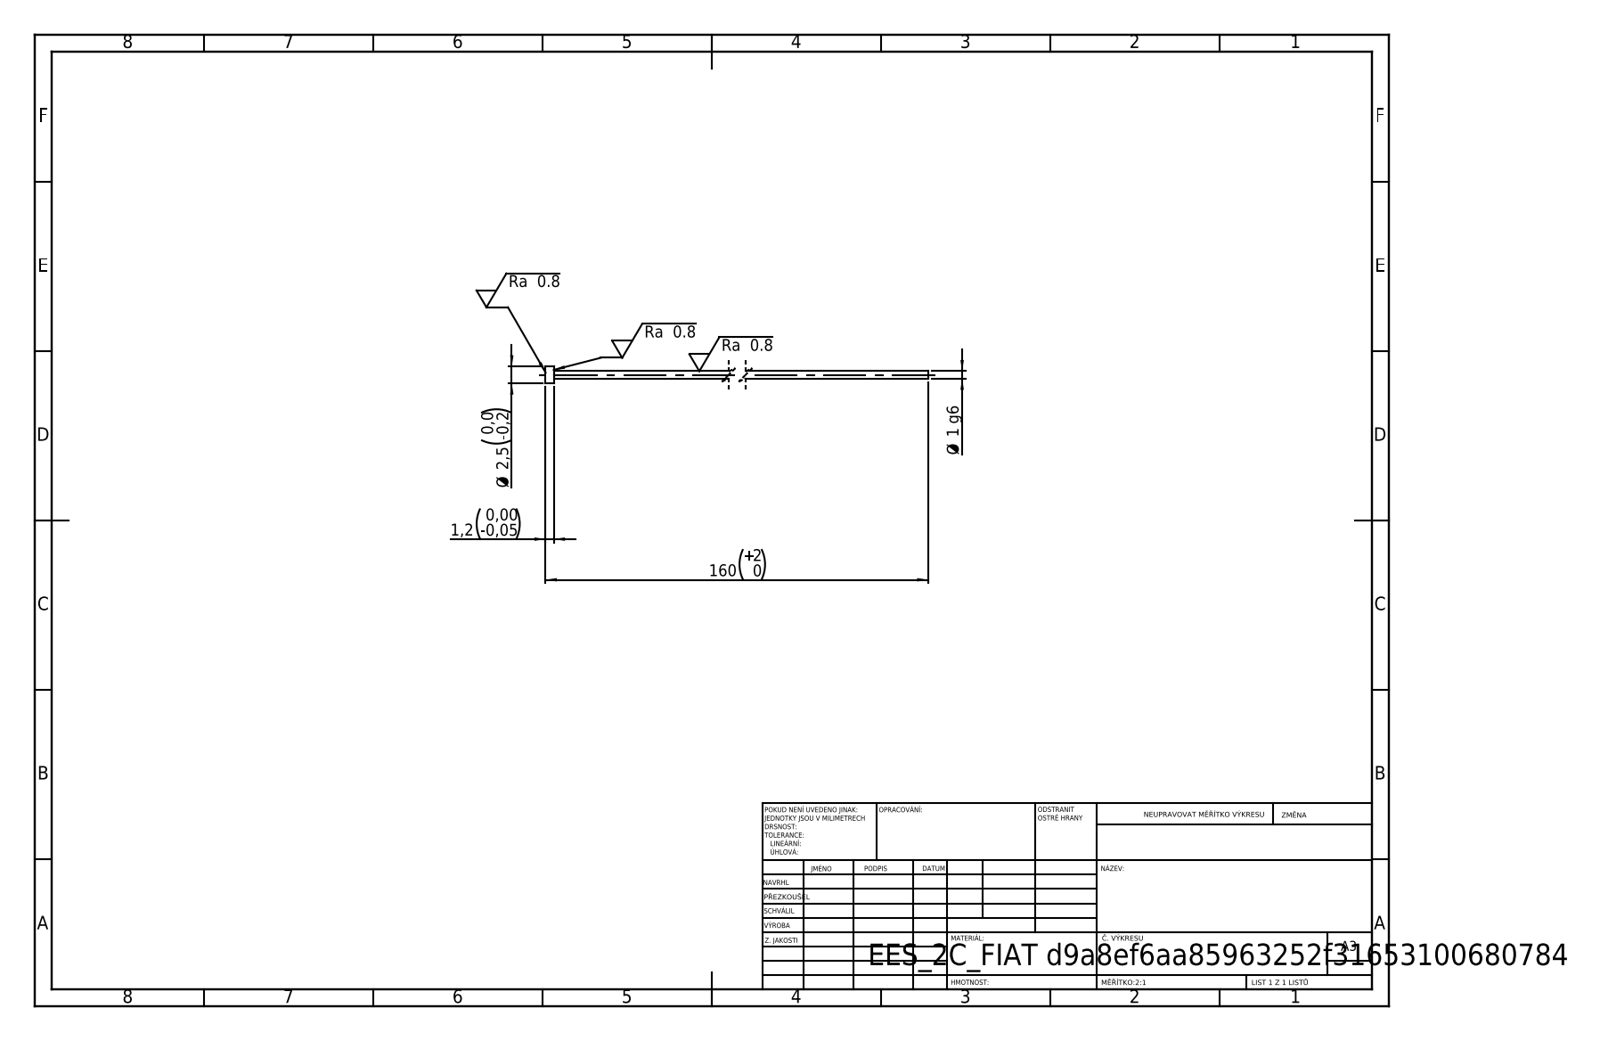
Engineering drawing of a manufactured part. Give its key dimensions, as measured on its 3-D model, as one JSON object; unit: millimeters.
{"step_written_by": "SolidWorks 2019 (CONFIG_CONTROL_DESIGN)", "units": "millimeters", "bodies": {"solids": 1, "faces": 7, "planar": 3, "cylindrical": 4, "other": 0}, "overall_size": [160, 2.5, 2.5], "volume_mm3": 157, "surface_area_mm2": 568, "round_bosses_or_shafts": [[2.5, 1], [1.1, 1]], "face_to_face_distances": [1.2, 160, 158.8]}
